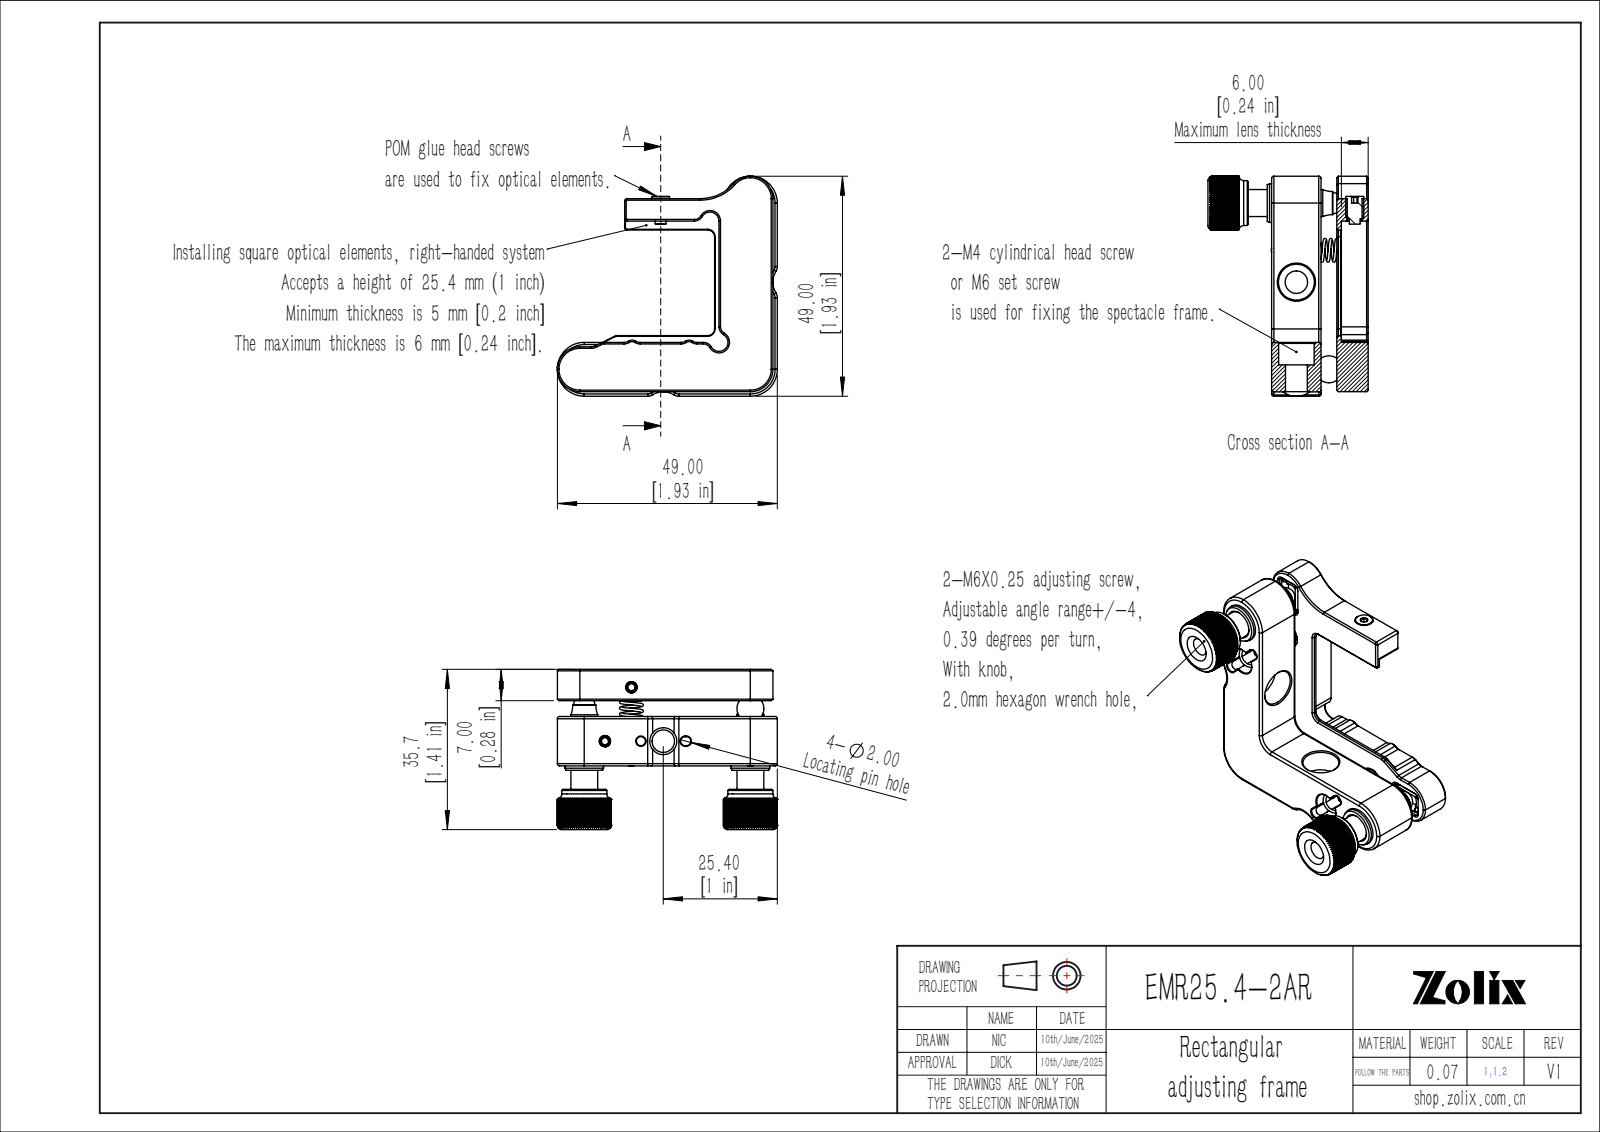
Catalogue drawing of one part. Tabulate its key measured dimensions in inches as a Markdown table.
| quantity | value |
| --- | --- |
| part name | EMR25.4-2AR |
| STEP written by | SolidWorks 2020 (CONFIG_CONTROL_DESIGN) |
| units | inches |
| bodies | 0 solids, 978 faces (474 planar, 296 cylindrical, 208 other) |
| overall size | 1.929 × 1.929 × 1.406 |
| round holes (diameter × count) | 0.236 × 5, 0.079 × 2, 0.157 × 2, 0.197 × 2, 0.315 × 2, 0.386 × 2, 0.13 × 1 |
| round bosses / shafts (diameter × count) | 0.059 × 4, 0.394 × 2, 0.339 × 2, 0.118 × 2, 0.079 × 2, 0.236 × 1, 0.157 × 1, 0.094 × 1 |
| partial cylindrical surfaces (radius × count) | 0.079 × 16, 0.02 × 11, 0.031 × 8, 0.039 × 4, 0.043 × 4, 0.059 × 4, 0.197 × 3, 0.236 × 3 |
| main face-to-face distances | 0.433, 0.276, 0.039, 0.413, 0.138, 0.472, 0.846, 0.571, 0.236, 0.197 |
| hole center spacings | 0.197, 0.413, 1.792, 0.512, 0.54, 1.476, 2.06 |
